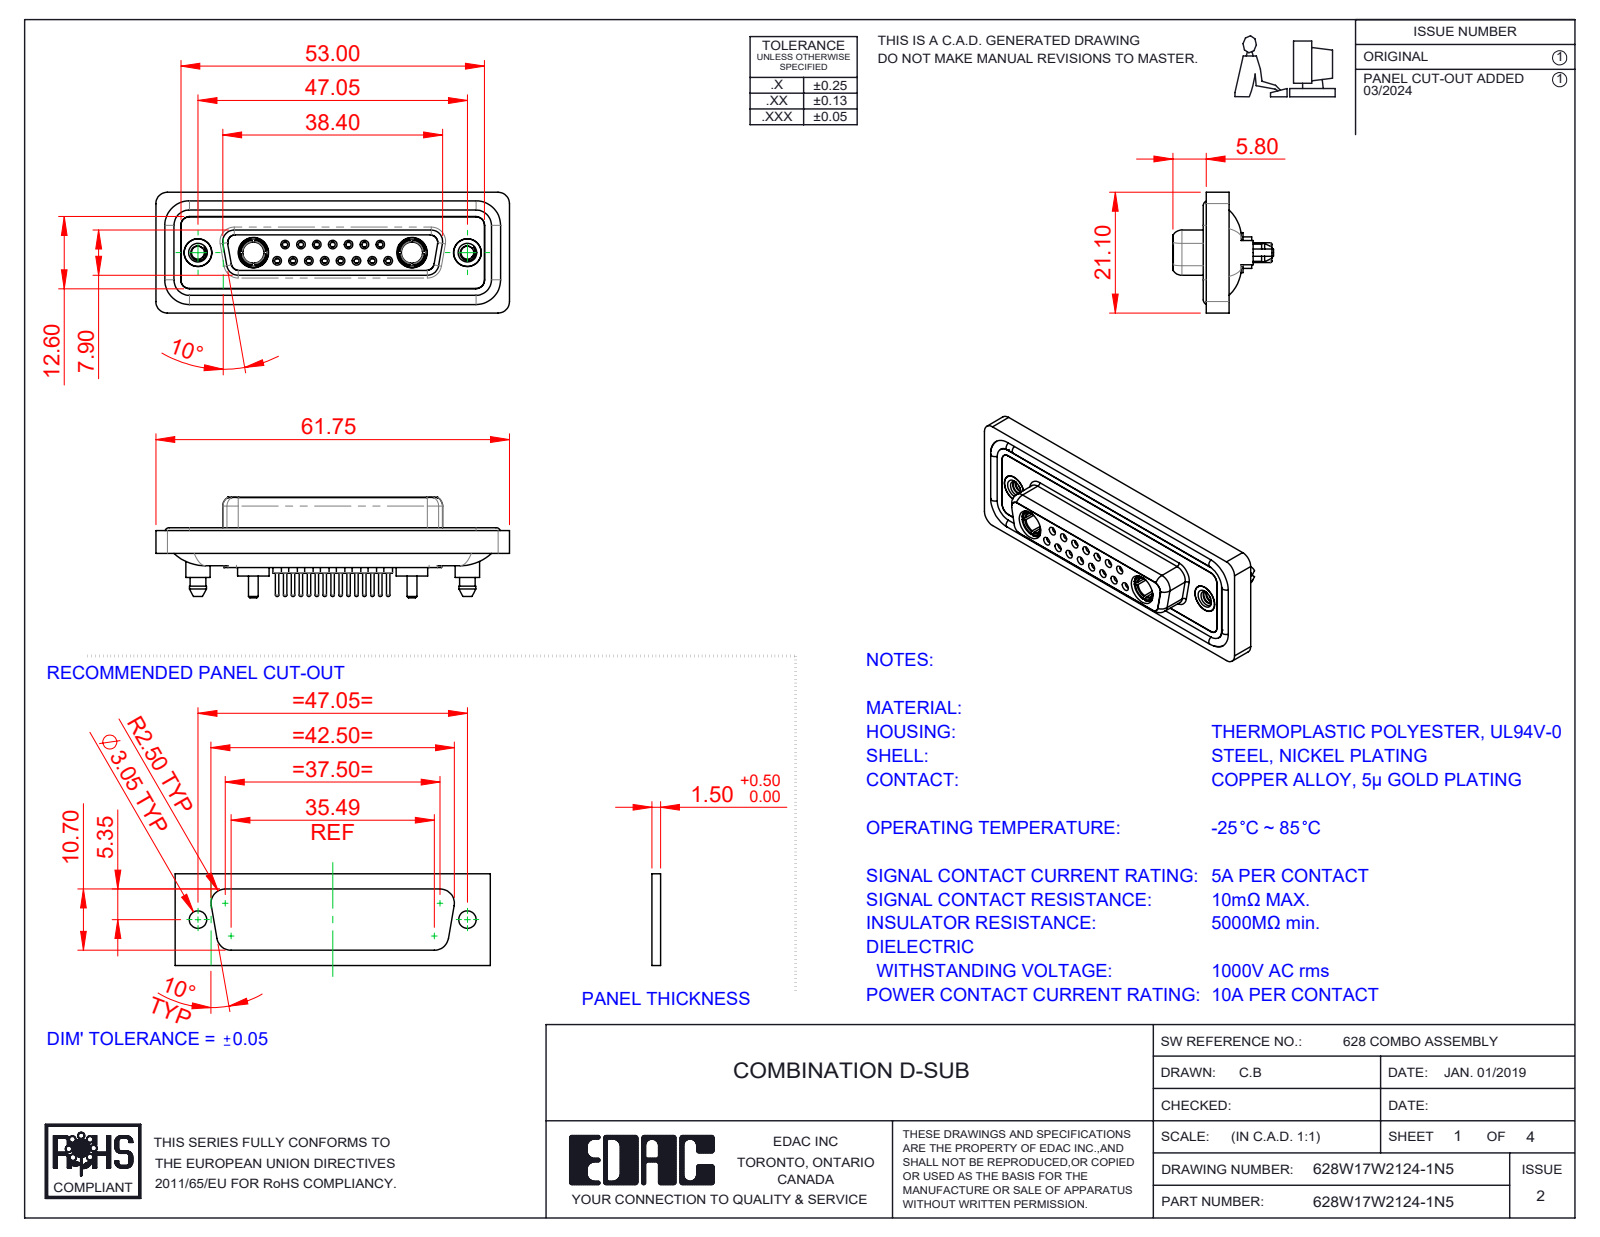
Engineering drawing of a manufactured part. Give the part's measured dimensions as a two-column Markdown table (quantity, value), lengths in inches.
| quantity | value |
| --- | --- |
| part name | Power Socket_10A S; 628Combo Shell Rear_25 Contacts; 628W17W2124-1N5; 628Combo Waterproof Housing_25 Contacts (+5 more) |
| STEP written by | SolidWorks 2023 (CONFIG_CONTROL_DESIGN) |
| units | inches |
| bodies | 26 solids, 1409 faces (404 planar, 551 cylindrical, 454 other) |
| overall size | 2.431 × 0.831 × 0.691 |
| volume | 0.514 in³ |
| surface area | 21.95 in² |
| round holes (diameter × count) | 0.035 × 15, 0.043 × 15, 0.059 × 15, 0.079 × 15, 0.063 × 8, 0.067 × 7, 0.191 × 4, 0.089 × 2, 0.146 × 2, 0.157 × 2, 0.159 × 2, 0.197 × 2 |
| round bosses / shafts (diameter × count) | 0.087 × 15, 0.024 × 15, 0.063 × 11, 0.217 × 2, 0.213 × 2, 0.205 × 2, 0.195 × 2, 0.195 × 2 |
| partial cylindrical surfaces (radius × count) | 0.059 × 24, 0.079 × 18, 0.063 × 10, 0.053 × 8, 0.01 × 4, 0.02 × 4, 0.024 × 4, 0.026 × 4 |
| main face-to-face distances | 0.016, 0.071, 0.293, 0.222, 0.26, 0.02, 0.278, 0.063, 0.114, 0.043 |
| hole center spacings | 0.124, 0.109, 0.327, 0.218, 0.198, 0.198, 0.295, 0.436 |
